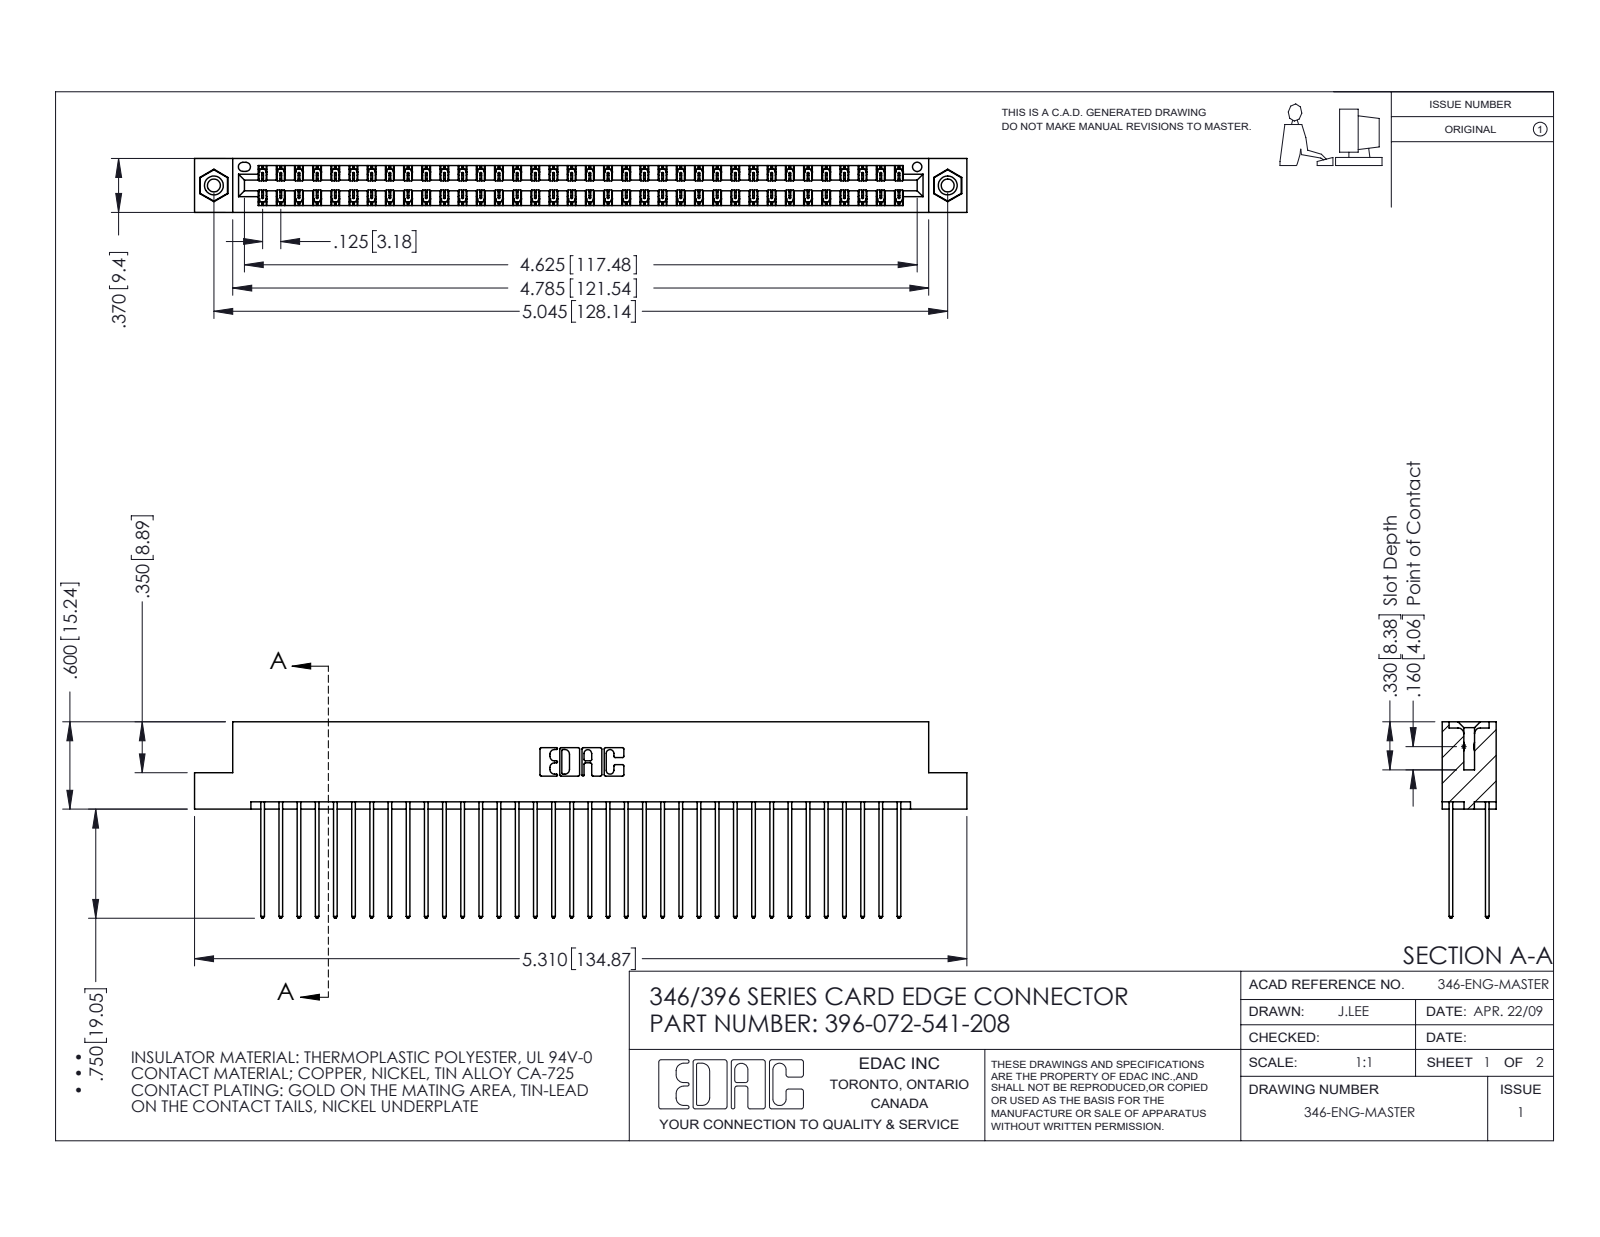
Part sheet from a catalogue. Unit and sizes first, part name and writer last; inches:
Units: inches
Overall size (bounding box): 5.31 × 1.35 × 0.37
Round holes (diameter × count): ⌀0.089 ×2, ⌀0.125 ×2, ⌀0.156 ×2, ⌀0.064 ×1
Round bosses / shafts (diameter × count): ⌀0.155 ×2
Partial cylindrical surfaces — rounded edges, fillets, slot ends (radius × count): R0.006 ×108, R0.01 ×72, R0.01 ×22, R0.007 ×6, R0.031 ×6, R0.026 ×3, R0.014 ×2, R0.022 ×2
Main face-to-face distances: 0.048, 0.322, 0.25, 0.072, 0.298, 0.025, 0.37, 0.275, 0.225, 0.148
Hole centre spacings: 0.246, 4.836, 5.045
Volume: 0.825 in³ · Surface area: 31.74 in²
Bodies: 75 solids, 3926 faces (2628 planar, 1282 cylindrical, 16 other)
Part name (STEP PRODUCT): 345-292-001_345-293-141; 346 Part_Flush Mounting Lugs - 0.156 Dia-TI; 396-072-541-208; 345-250-001_345-250-003-102
STEP written by: SolidWorks 2016 (CONFIG_CONTROL_DESIGN)
